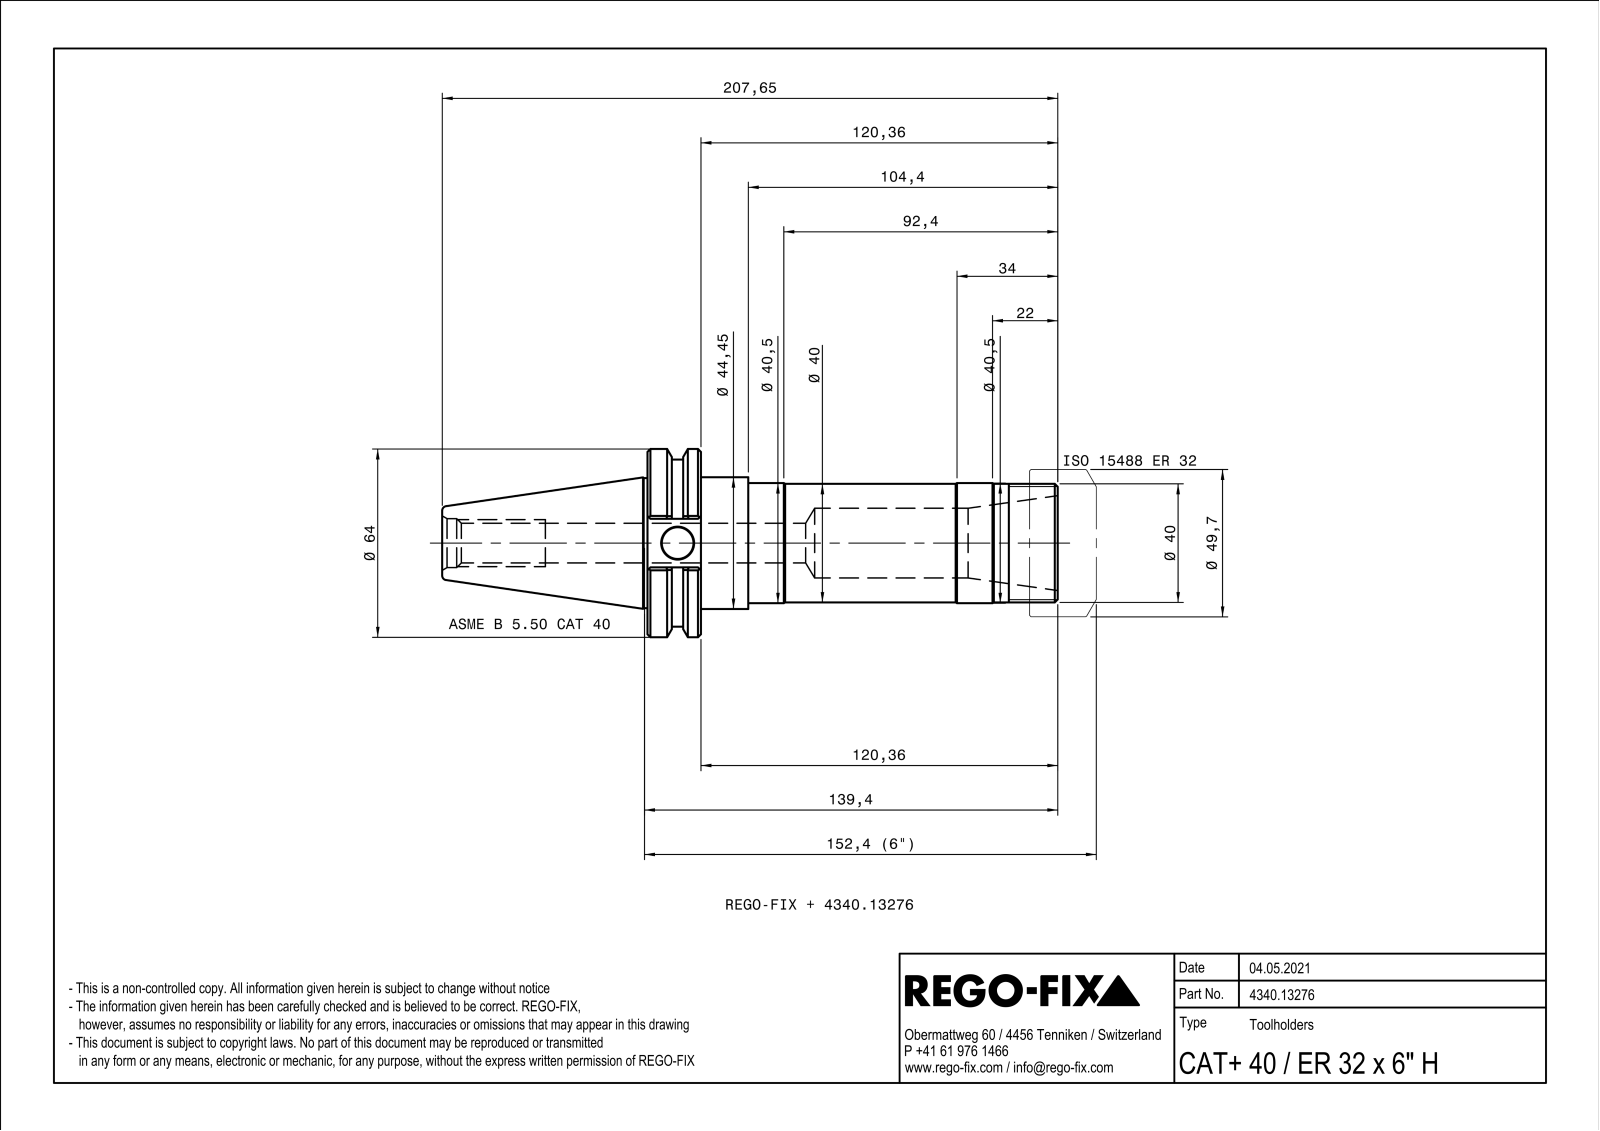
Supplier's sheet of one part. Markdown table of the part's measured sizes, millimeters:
| quantity | value |
| --- | --- |
| part name | NOCUT |
| STEP written by | SIEMENS PLM Software Solid Edge ST10 (AUTOMOTIVE_DESIGN) |
| units | millimeters |
| bodies | 2 solids, 239 faces (70 planar, 67 cylindrical, 102 other) |
| overall size | 208.05 × 63.8 × 63.5 |
| volume | 429 224 mm³ |
| surface area | 87 995 mm² |
| round holes (diameter × count) | 3.9 × 2, 12 × 2, 3.24 × 1, 13.38 × 1, 16.2 × 1, 16.5 × 1, 23.5 × 1 |
| round bosses / shafts (diameter × count) | 63.8 × 1, 63.5 × 1, 56.36 × 1, 44.75 × 1, 44.45 × 1, 43.85 × 1, 40.8 × 1, 40.5 × 1 |
| partial cylindrical surfaces (radius × count) | 0.5 × 8, 2.25 × 2 |
| main face-to-face distances | 18.05, 18.25, 138.6, 47.33, 120.55, 138.8, 120.35, 138.4, 16.68, 33.06 |
